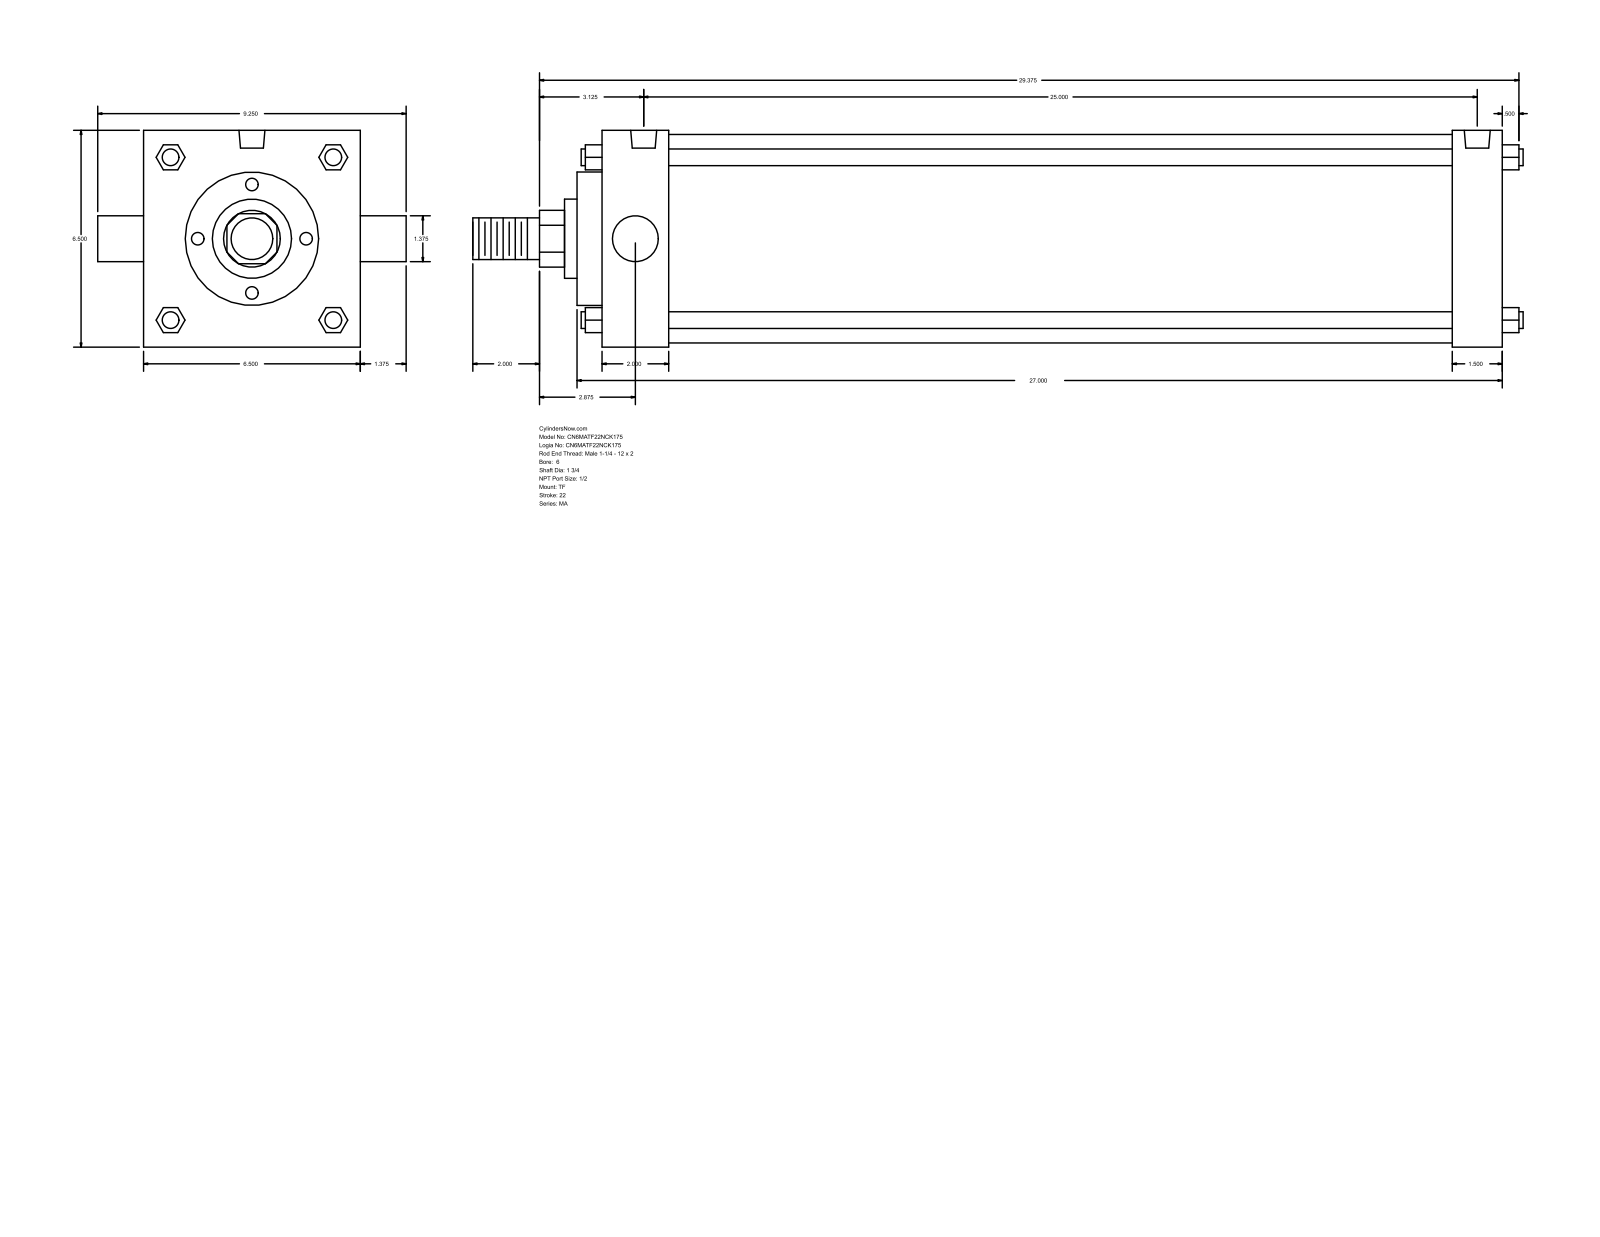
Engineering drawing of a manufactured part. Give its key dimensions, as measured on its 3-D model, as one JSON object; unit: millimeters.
{"part_name": "MA_TF__0600_1.75", "step_written_by": "GSSL Pune (CONFIG_CONTROL_DESIGN)", "units": "millimeters", "bodies": {"solids": 0, "faces": 122, "planar": 93, "cylindrical": 29, "other": 0}, "overall_size": [800.1, 234.95, 165.1], "round_holes": [[17.46, 3], [19.77, 2]], "round_bosses_or_shafts": [[12.7, 4], [158.75, 1], [101.6, 1], [60.33, 1], [44.45, 1], [34.92, 1], [31.75, 1]], "partial_cylinders_radius": [[21.63, 1]], "face_to_face_distances": [165.1, 685.8, 19.05, 50.8, 635, 647.71, 596.91, 38.09, 69.85, 666.76], "hole_center_spacings": [635]}
